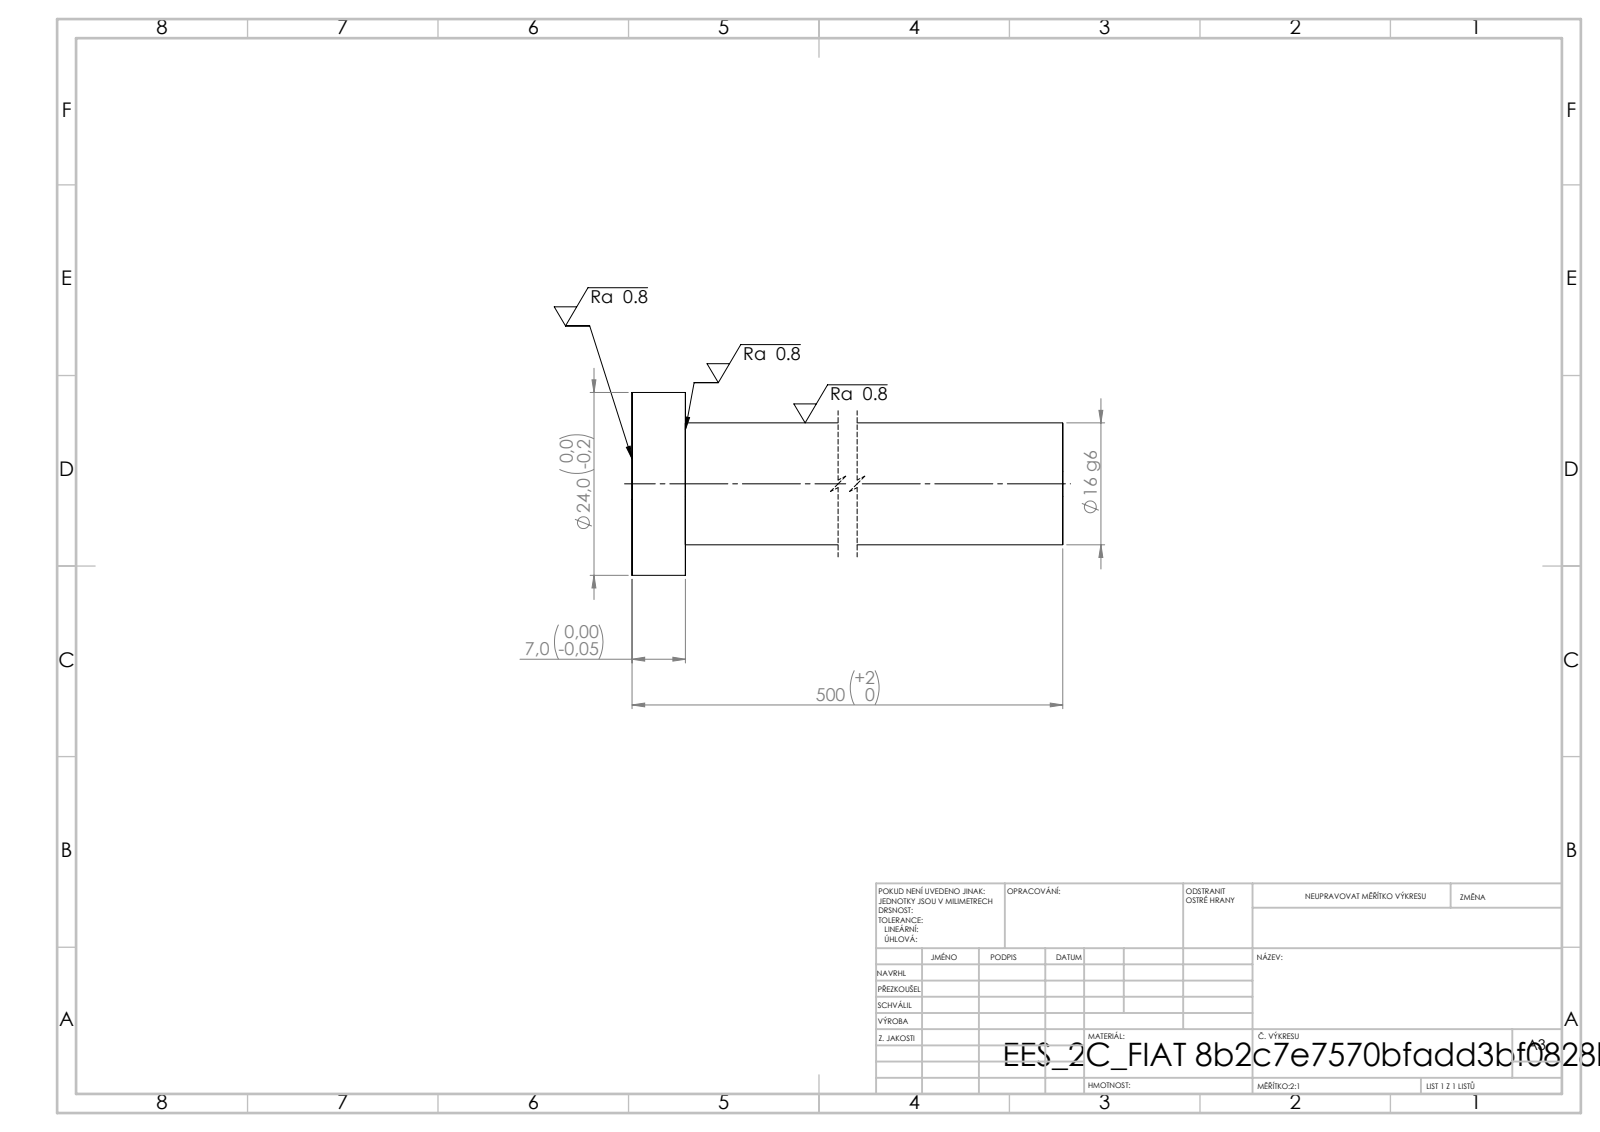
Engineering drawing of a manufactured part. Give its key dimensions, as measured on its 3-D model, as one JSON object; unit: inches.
{"step_written_by": "SolidWorks 2019 (CONFIG_CONTROL_DESIGN)", "units": "inches", "bodies": {"solids": 1, "faces": 7, "planar": 3, "cylindrical": 4, "other": 0}, "overall_size": [19.685, 0.945, 0.945], "volume_in3": 6.242, "surface_area_in2": 40.63, "round_bosses_or_shafts": [[0.945, 1], [0.63, 1]], "face_to_face_distances": [0.276, 19.685, 19.409]}
